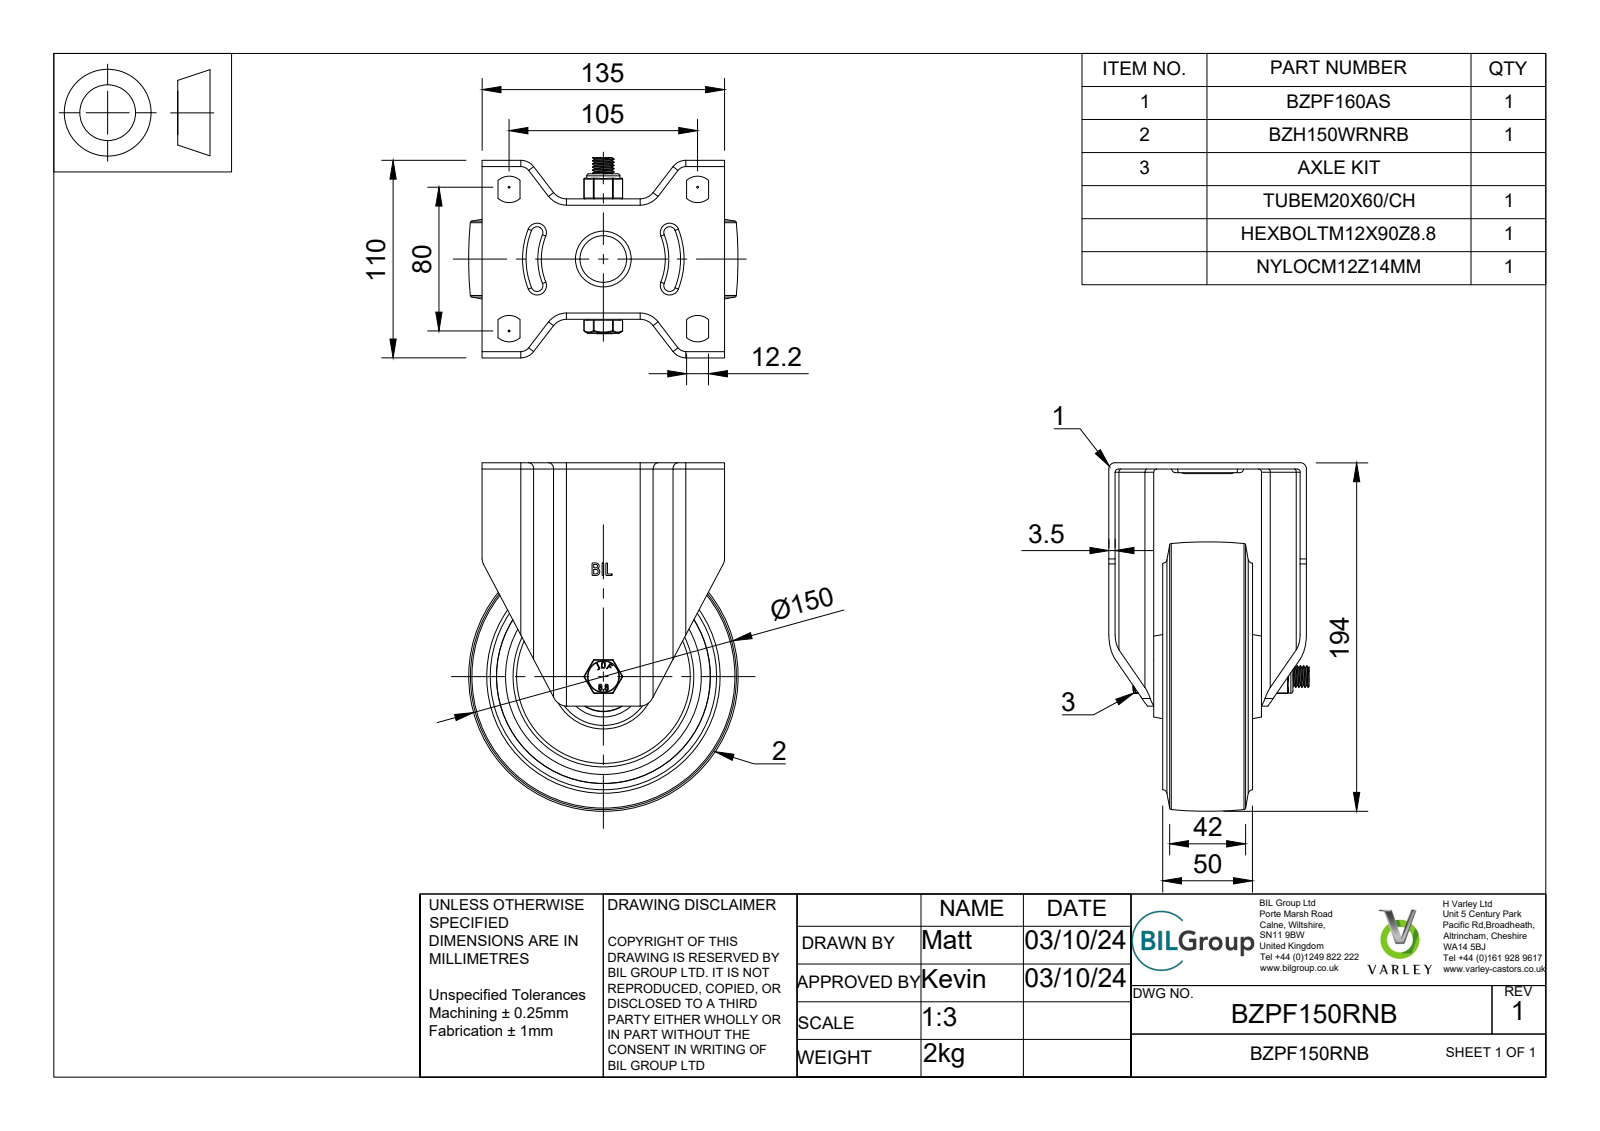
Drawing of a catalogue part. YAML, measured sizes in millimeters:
part_name: "BZPF150RNB v3; BZPF160AS v1; ZINC PLATED, PRESSED STEEL BRACKET; BZH150WRNRB v1 (+8 more)"
step_written_by: "Autodesk Translation Framework v13.20.0.188 (AUTOMOTIVE_DESIGN)"
units: millimeters
bodies: {solids: 16, faces: 496, planar: 213, cylindrical: 169, other: 114}
overall_size: [194, 150, 111.5]
volume: 728201
surface_area: 238756
round_holes:
  - {diameter: 12, count: 1}
  - {diameter: 12.2, count: 1}
  - {diameter: 12.5, count: 1}
  - {diameter: 14, count: 1}
  - {diameter: 20, count: 1}
  - {diameter: 30, count: 1}
  - {diameter: 39, count: 1}
  - {diameter: 119, count: 1}
round_bosses_or_shafts:
  - {diameter: 5, count: 8}
  - {diameter: 19.9, count: 1}
  - {diameter: 18.5, count: 1}
  - {diameter: 17.75, count: 1}
  - {diameter: 11.83, count: 1}
  - {diameter: 9.84, count: 1}
partial_cylinders:
  - {radius: 0.5, count: 20}
  - {radius: 1.75, count: 8}
  - {radius: 3.5, count: 8}
  - {radius: 9, count: 8}
  - {radius: 9.09, count: 8}
  - {radius: 0.47, count: 4}
  - {radius: 0.9, count: 4}
  - {radius: 5.5, count: 4}
face_to_face_distances: [3.5, 21.5, 85, 63.5, 33, 30.5, 36.5, 27, 2.34, 52]
